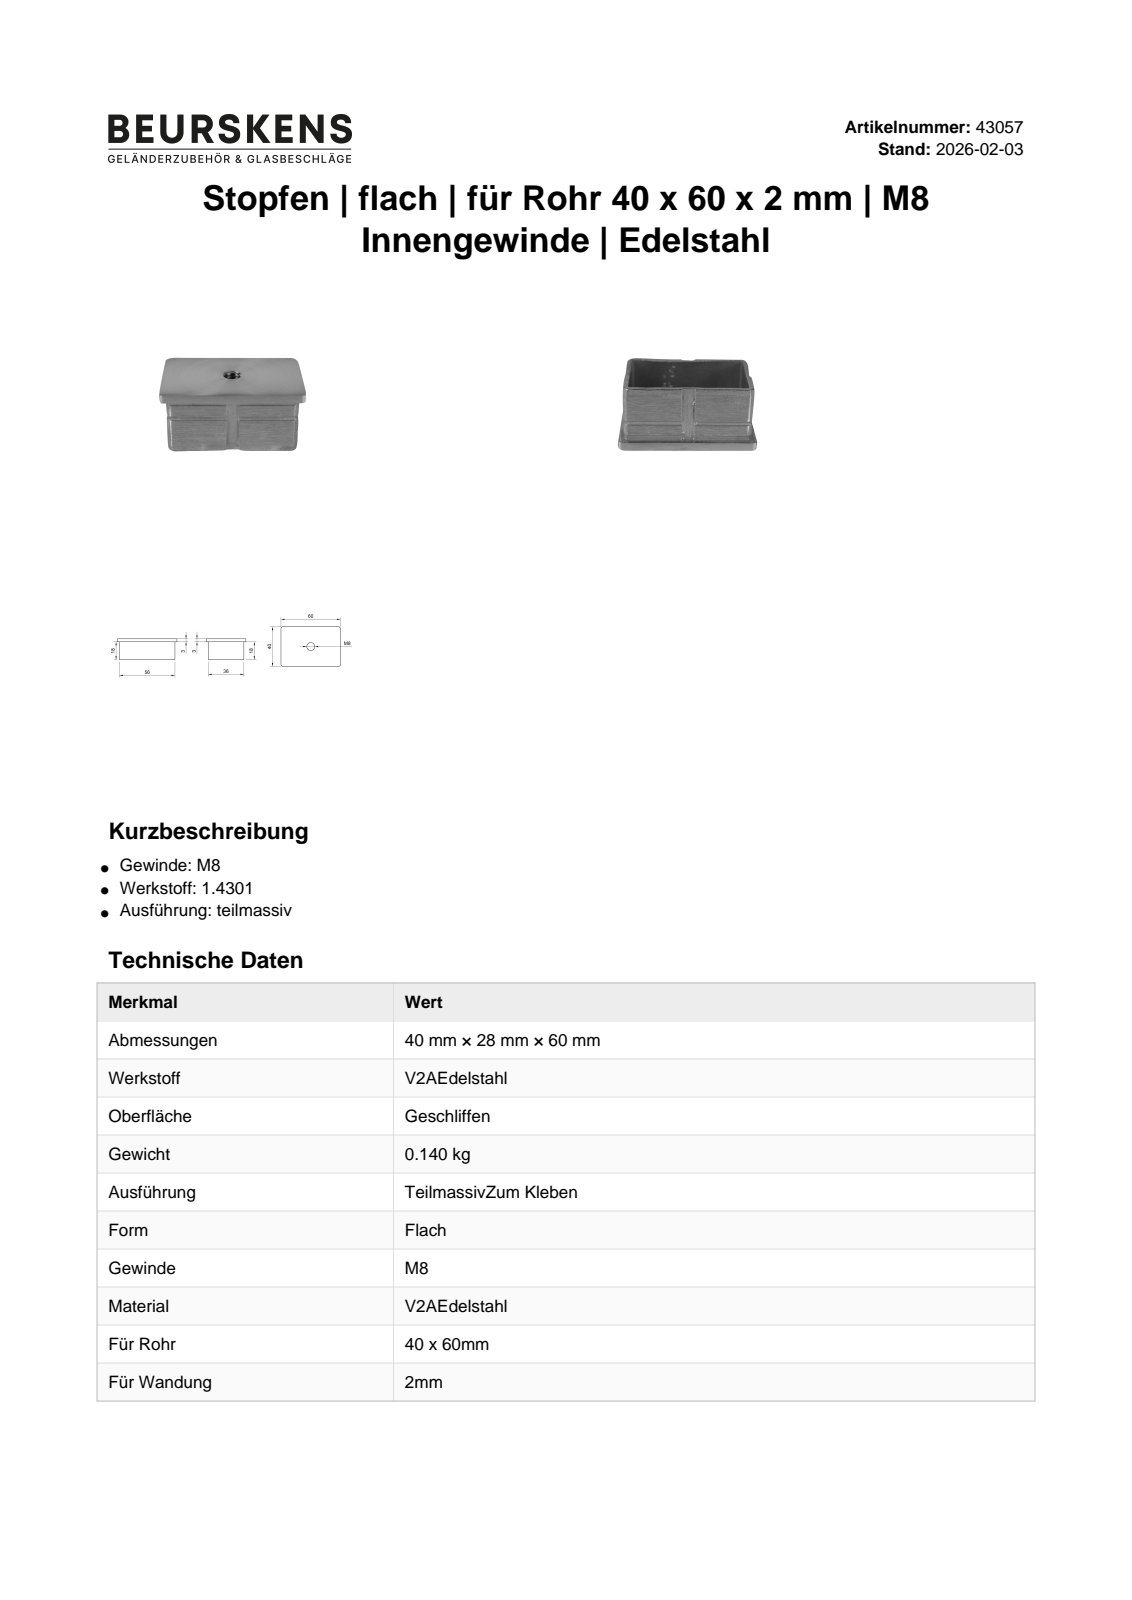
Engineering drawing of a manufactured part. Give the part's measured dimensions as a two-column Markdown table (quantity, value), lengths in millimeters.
| quantity | value |
| --- | --- |
| part name | 43057 |
| STEP written by | Autodesk Inventor 2022 (AUTOMOTIVE_DESIGN) |
| units | millimeters |
| bodies | 1 solid, 27 faces (17 planar, 10 cylindrical, 0 other) |
| overall size | 60 × 40 × 21 |
| volume | 12 058 mm³ |
| surface area | 12 252 mm² |
| round holes (diameter × count) | 8 × 1 |
| round bosses / shafts (diameter × count) | 11 × 1 |
| partial cylindrical surfaces (radius × count) | 2 × 8 |
| main face-to-face distances | 2, 34, 36, 54, 32, 56, 52, 4, 1, 3 |
